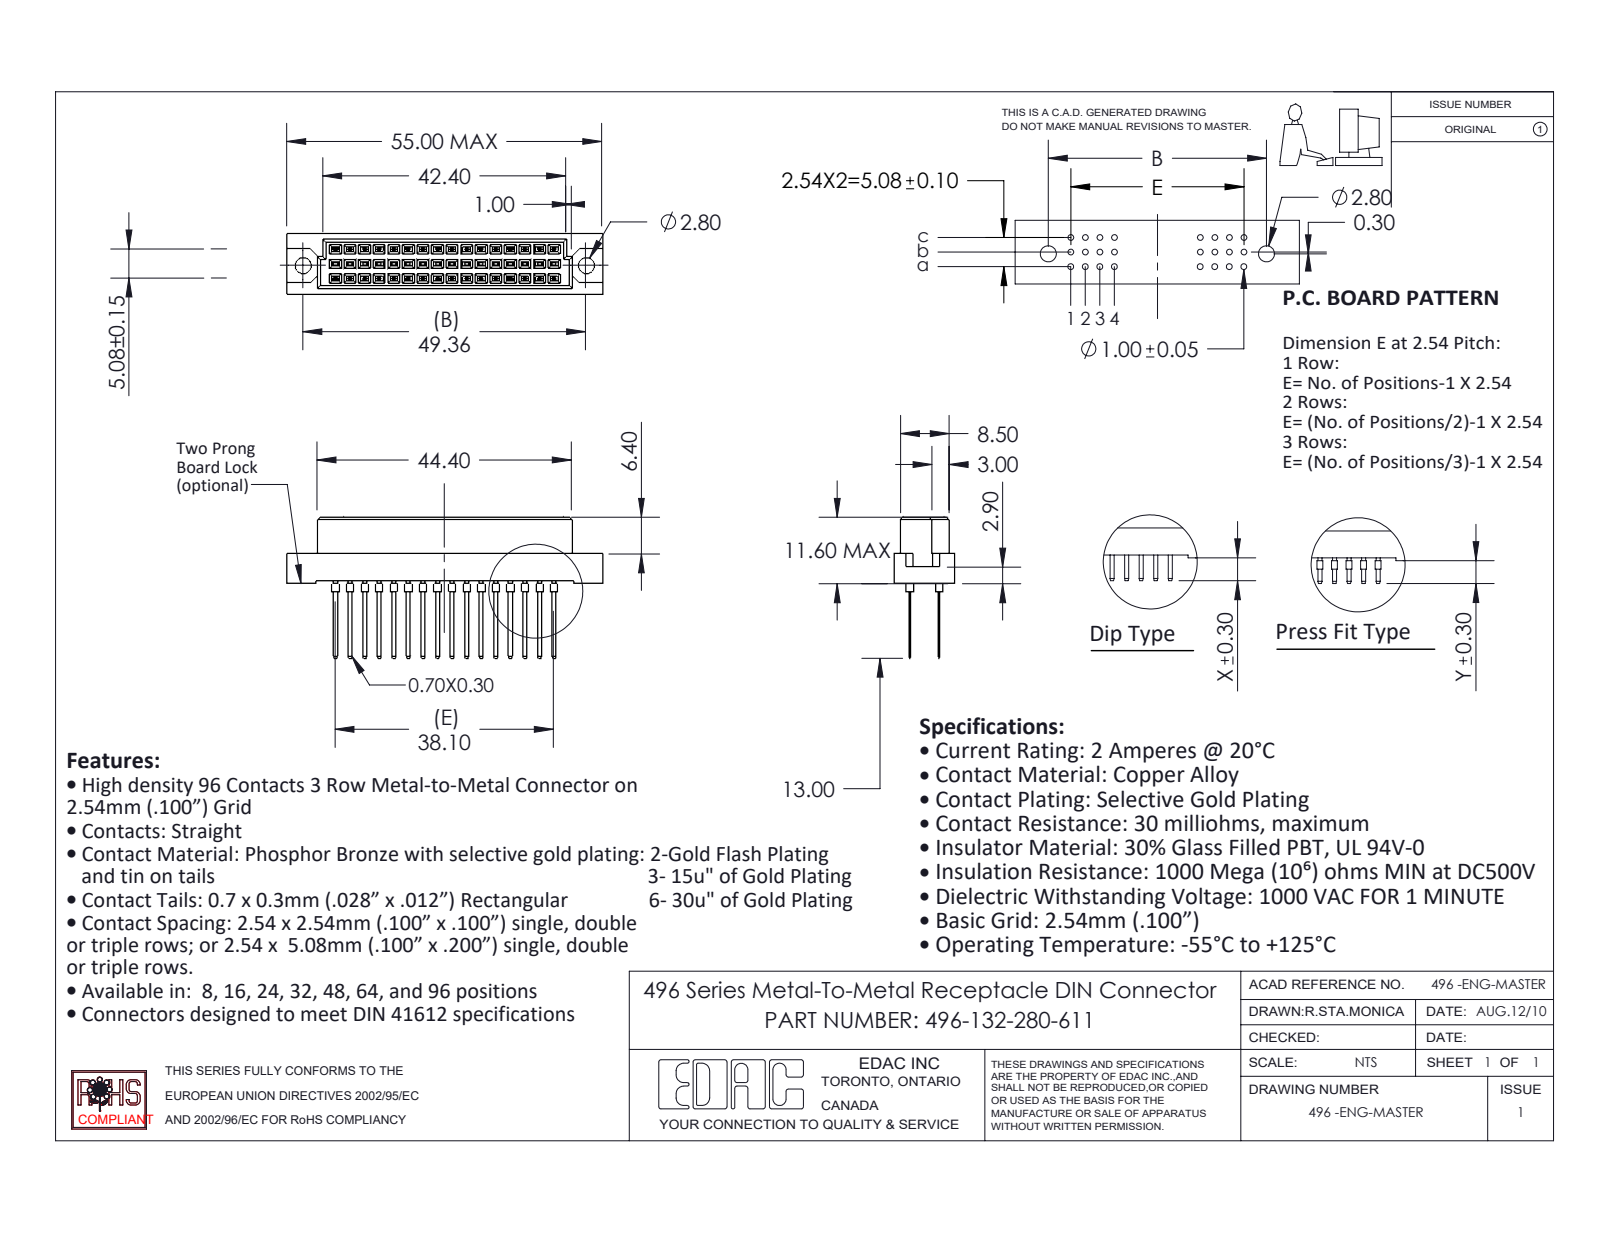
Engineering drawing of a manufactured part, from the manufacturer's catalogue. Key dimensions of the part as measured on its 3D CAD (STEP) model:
Part name (STEP PRODUCT): 496-290_80; 496-132-280-611; 496 Part_48
STEP written by: SolidWorks 2020 (CONFIG_CONTROL_DESIGN)
Units: millimetres
Bodies: 33 solids, 1242 faces (1174 planar, 68 cylindrical, 0 other)
Overall size (bounding box): 55 × 24.6 × 10.6
Volume: 4 732 mm³ · Surface area: 5 416 mm²
Round holes (diameter × count): ⌀2.8 ×2
Round bosses / shafts (diameter × count): ⌀1 ×32
Main face-to-face distances: 2.54, 5.08, 1.05, 9.55, 2.61, 2.91, 7.69, 7.99, 1.56, 1.86
Hole centre spacings: 49.36
